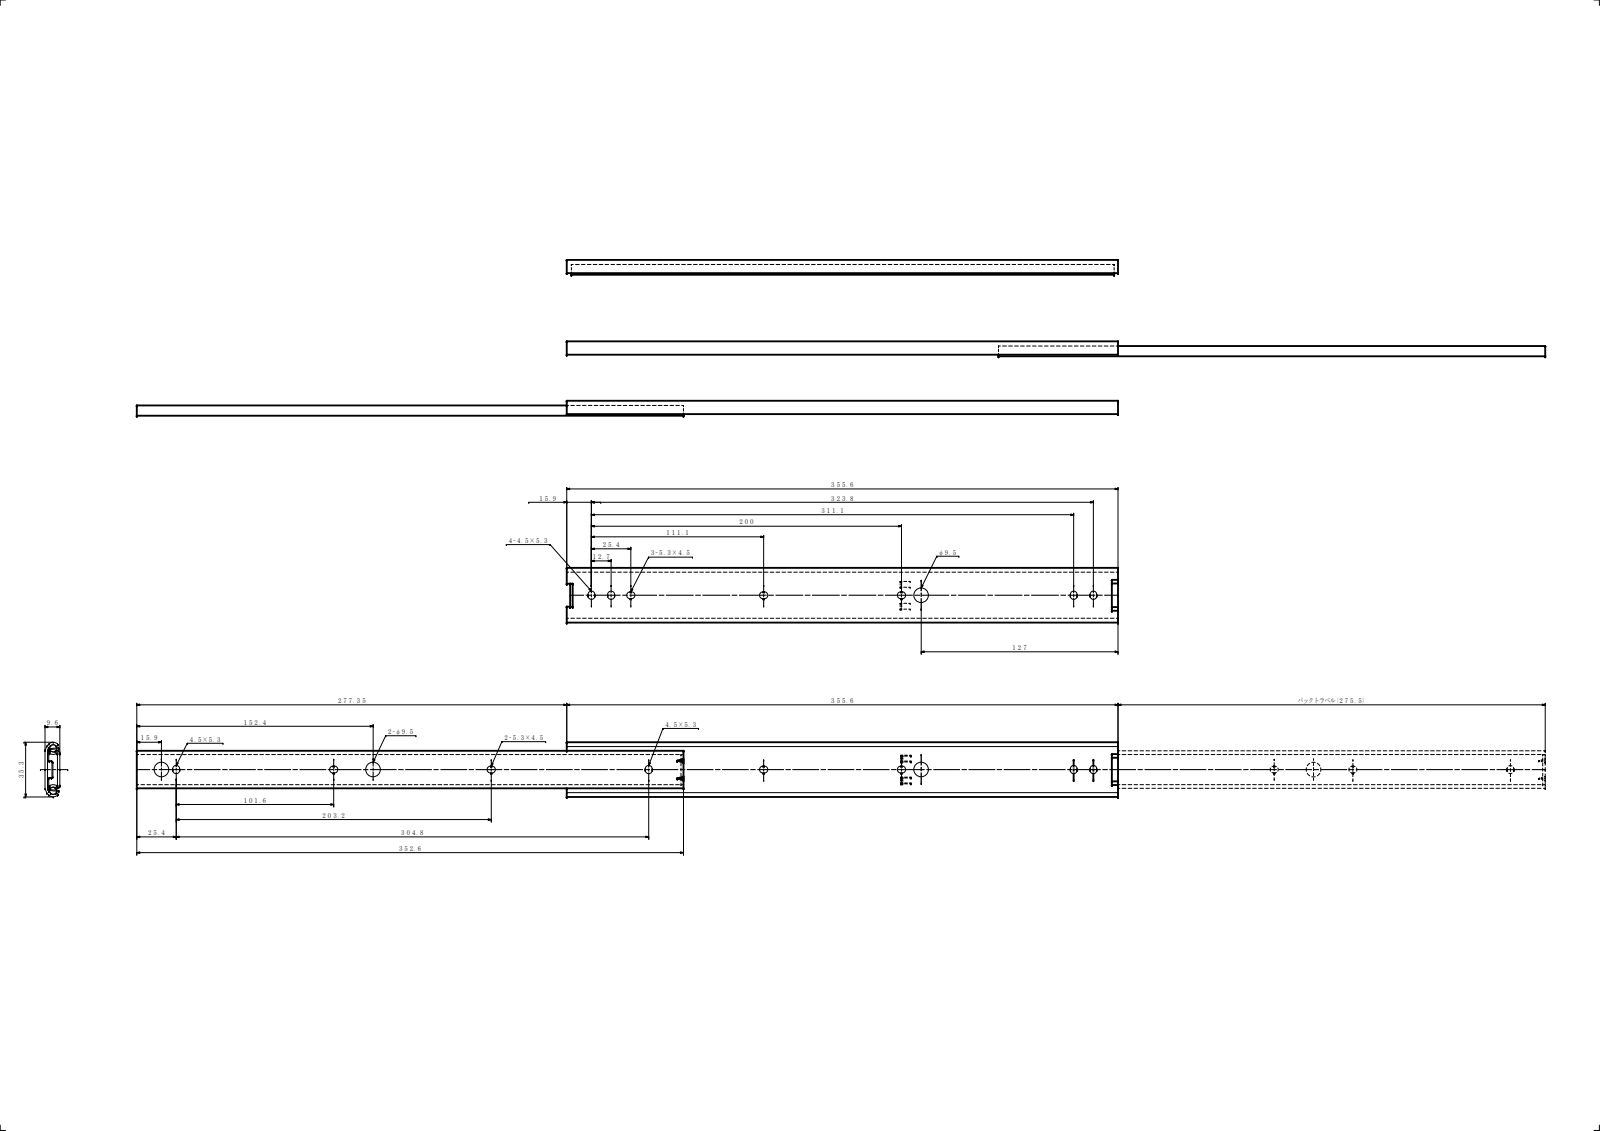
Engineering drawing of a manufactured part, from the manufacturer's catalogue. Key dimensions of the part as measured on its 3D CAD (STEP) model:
Part name (STEP PRODUCT): 3520-14; IM 3520-14; OM 3520-14
STEP written by: SolidWorks 2019 (CONFIG_CONTROL_DESIGN)
Units: millimetres
Bodies: 2 solids, 138 faces (68 planar, 70 cylindrical, 0 other)
Overall size (bounding box): 632.95 × 35.3 × 9.6
Volume: 44 289 mm³ · Surface area: 58 345 mm²
Round holes (diameter × count): ⌀9.5 ×3
Partial cylindrical surfaces — rounded edges, fillets, slot ends (radius × count): R2.25 ×22, R0.4 ×6, R1 ×4, R2.5 ×4, R3 ×4, R0.2 ×2, R1.8 ×2, R2 ×2
Main face-to-face distances: 1.6, 8, 9.6, 6.4, 1.3, 6.7, 2.9, 5.1, 4.67, 3.07
Hole centre spacings: 136.5, 353.55, 490.05
